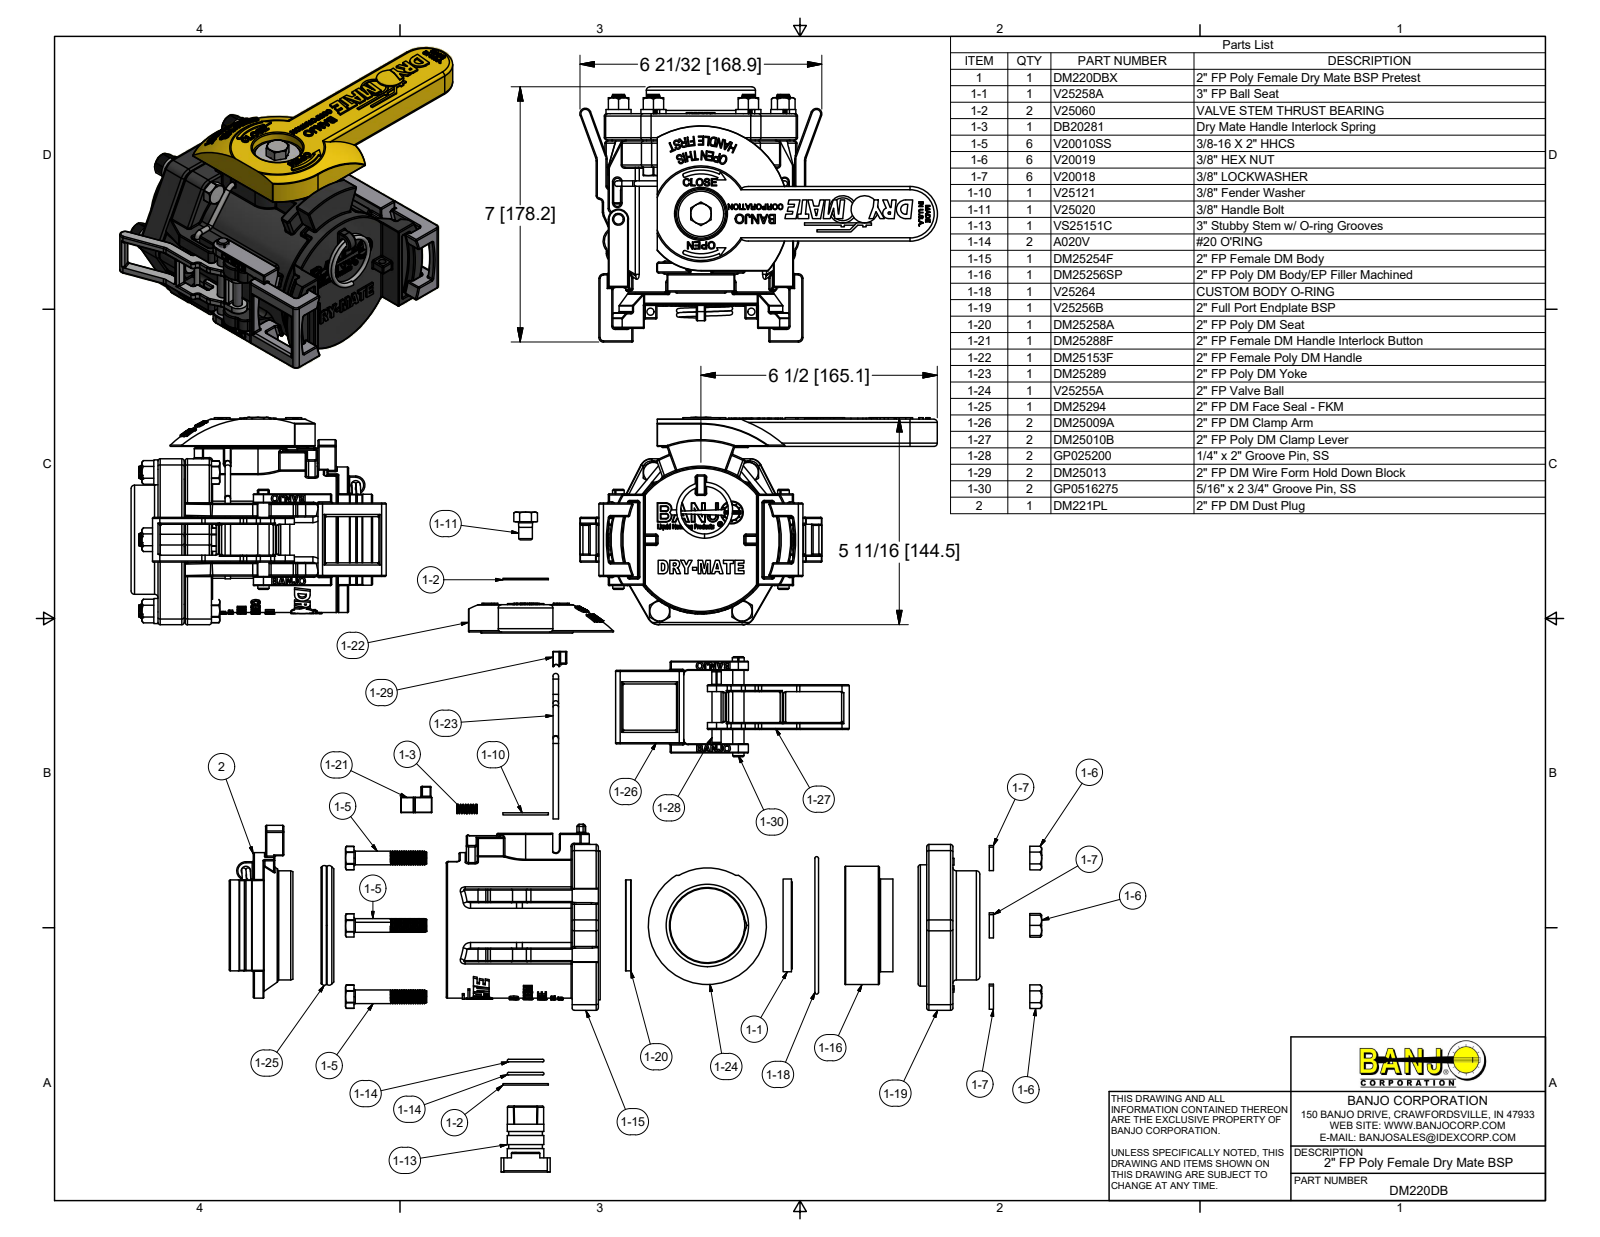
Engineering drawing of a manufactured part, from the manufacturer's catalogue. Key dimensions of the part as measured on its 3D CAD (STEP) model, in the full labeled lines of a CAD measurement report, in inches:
Part name (STEP PRODUCT): DM220DB; DM220DBX; DM25254F; DM25254FY (+8 more)
STEP written by: Autodesk Inventor 2017 (AUTOMOTIVE_DESIGN)
Units: inches
Bodies: 48 solids, 7077 faces (2459 planar, 1822 cylindrical, 2796 other)
Overall size (bounding box): 9.825 × 7.015 × 5.698
Volume: 50.49 in³ · Surface area: 613.6 in²
Round holes (diameter × count): ⌀0.406 ×7, ⌀0.307 ×6, ⌀0.385 ×6, ⌀0.45 ×6, ⌀0.25 ×3, ⌀0.2 ×2, ⌀0.313 ×2, ⌀0.32 ×2, ⌀2.05 ×2, ⌀0.307 ×1, ⌀0.417 ×1, ⌀0.59 ×1
Round bosses / shafts (diameter × count): ⌀0.324 ×90, ⌀0.15 ×8, ⌀0.375 ×7, ⌀0.687 ×6, ⌀0.325 ×2, ⌀0.311 ×2, ⌀0.26 ×2, ⌀4.1 ×1
Partial cylindrical surfaces — rounded edges, fillets, slot ends (radius × count): R0.03 ×436, R0.06 ×103, R0.01 ×51, R0.02 ×50, R0.125 ×19, R0.313 ×15, R0.25 ×14, R0.063 ×12
Main face-to-face distances: 0.75, 5.24, 0.25, 0.65, 4.54, 2, 0.05, 0.72, 0.03, 0.7
Hole centre spacings: 0.601, 2.085, 2.144, 2.263, 2.264, 2.265, 2.266, 2.275
